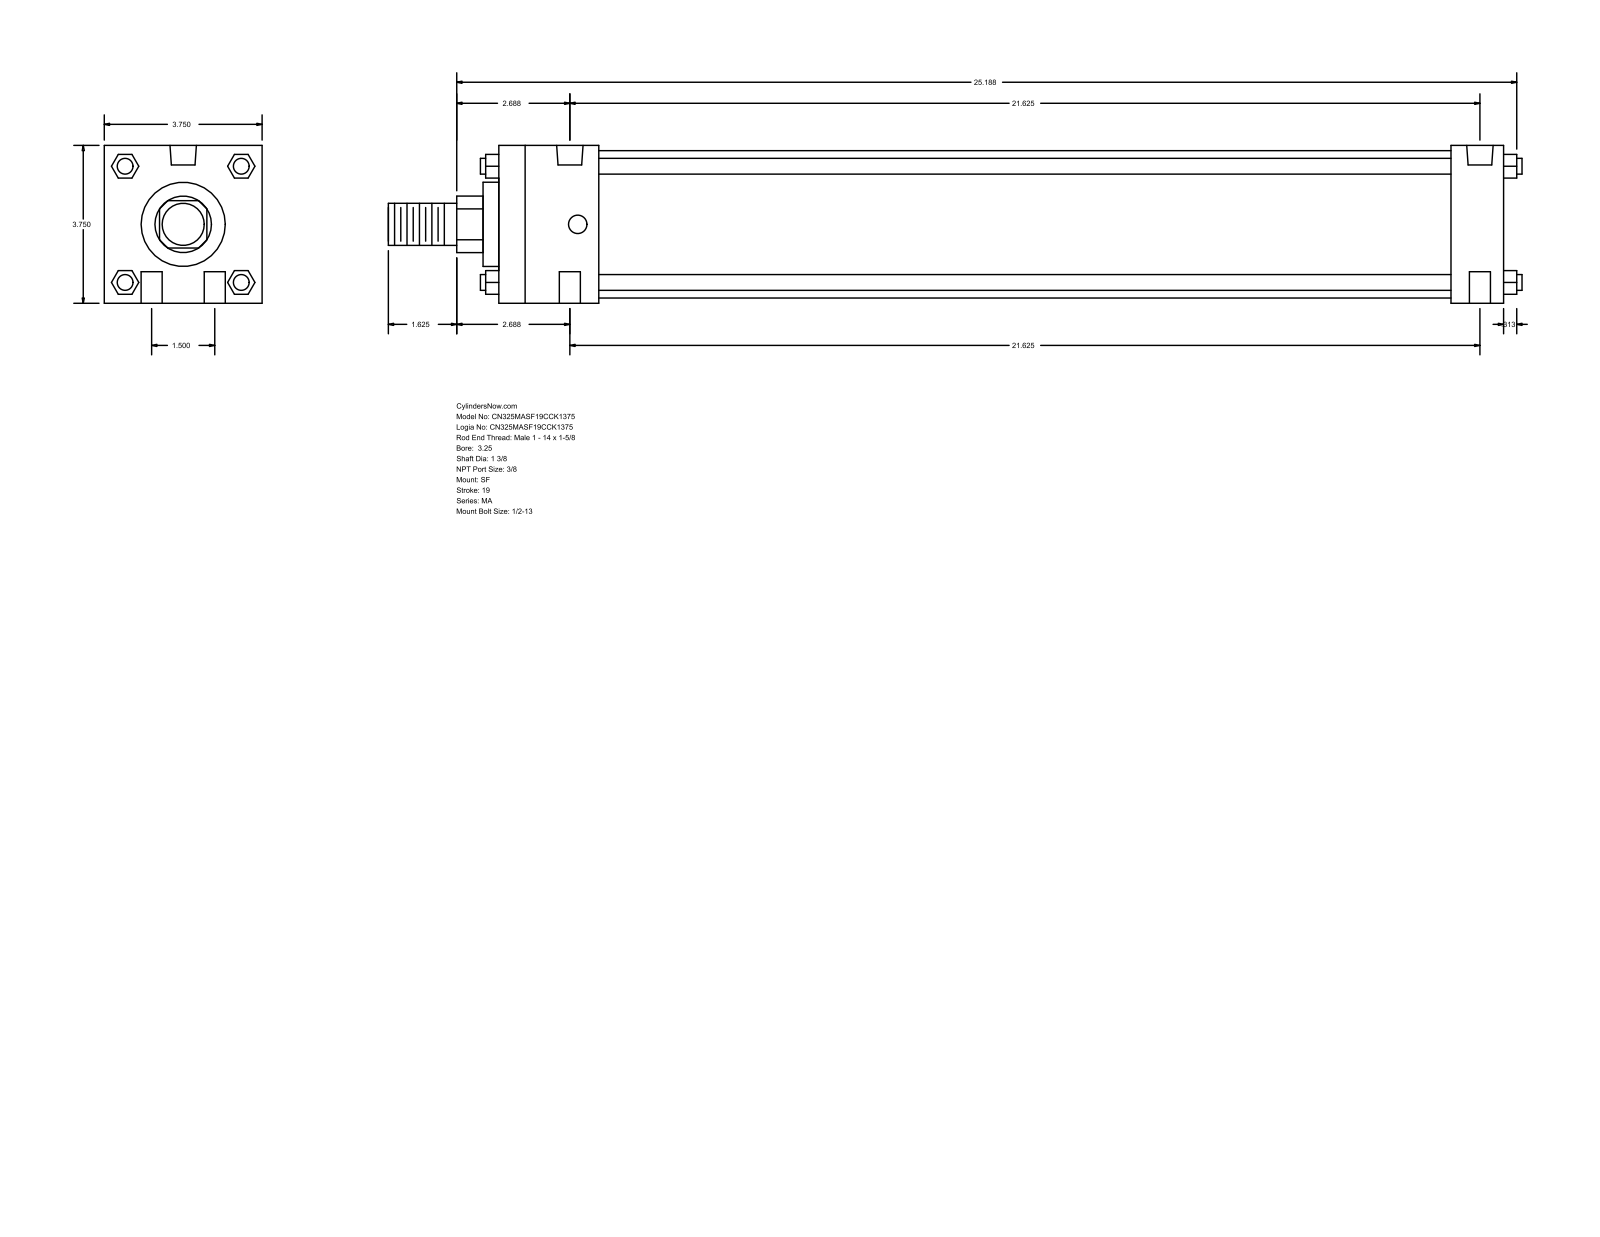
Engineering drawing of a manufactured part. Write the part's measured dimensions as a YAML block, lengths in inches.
part_name: "MA_SF__0325_1.375"
step_written_by: "GSSL Pune (CONFIG_CONTROL_DESIGN)"
units: inches
bodies: {solids: 0, faces: 124, planar: 94, cylindrical: 30, other: 0}
overall_size: [26.937, 3.75, 3.75]
round_holes:
  - {diameter: 0.5, count: 4}
  - {diameter: 0.437, count: 2}
  - {diameter: 0.627, count: 2}
round_bosses_or_shafts:
  - {diameter: 0.375, count: 4}
  - {diameter: 3.5, count: 1}
  - {diameter: 2, count: 1}
  - {diameter: 1.375, count: 1}
  - {diameter: 1, count: 1}
partial_cylinders:
  - {radius: 0.672, count: 1}
face_to_face_distances: [3.75, 23.875, 22.625, 1.25, 2.375, 20.25, 21.5, 0.375, 2.75, 23]
hole_center_spacings: [0.75, 21.638, 21.625, 1.5, 21.677, 21.25]
